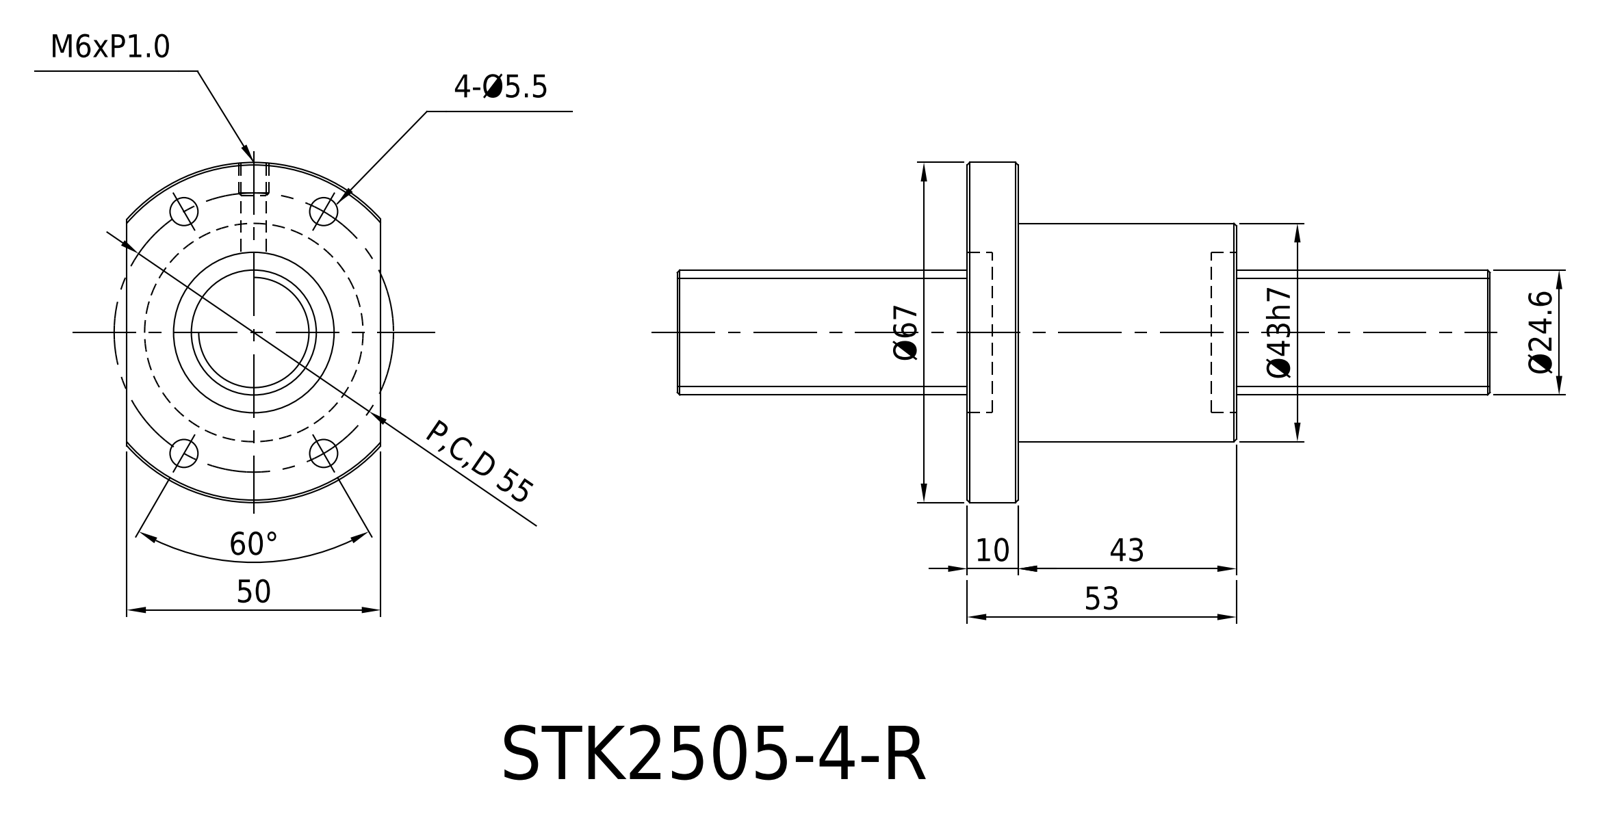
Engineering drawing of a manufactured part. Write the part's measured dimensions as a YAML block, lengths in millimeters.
part_name: "2505 STK"
step_written_by: "CATIA V5 STEP AP214 (AUTOMOTIVE_DESIGN)"
units: millimeters
bodies: {solids: 1, faces: 45, planar: 5, cylindrical: 14, other: 26}
overall_size: [67, 53, 50]
volume: 65453
surface_area: 17333
round_holes:
  - {diameter: 5.5, count: 4}
  - {diameter: 25, count: 1}
round_bosses_or_shafts:
  - {diameter: 43, count: 1}
partial_cylinders:
  - {radius: 33.5, count: 1}
face_to_face_distances: [10, 43, 53, 50]
hole_center_spacings: [27.5, 47.64, 55.01]
